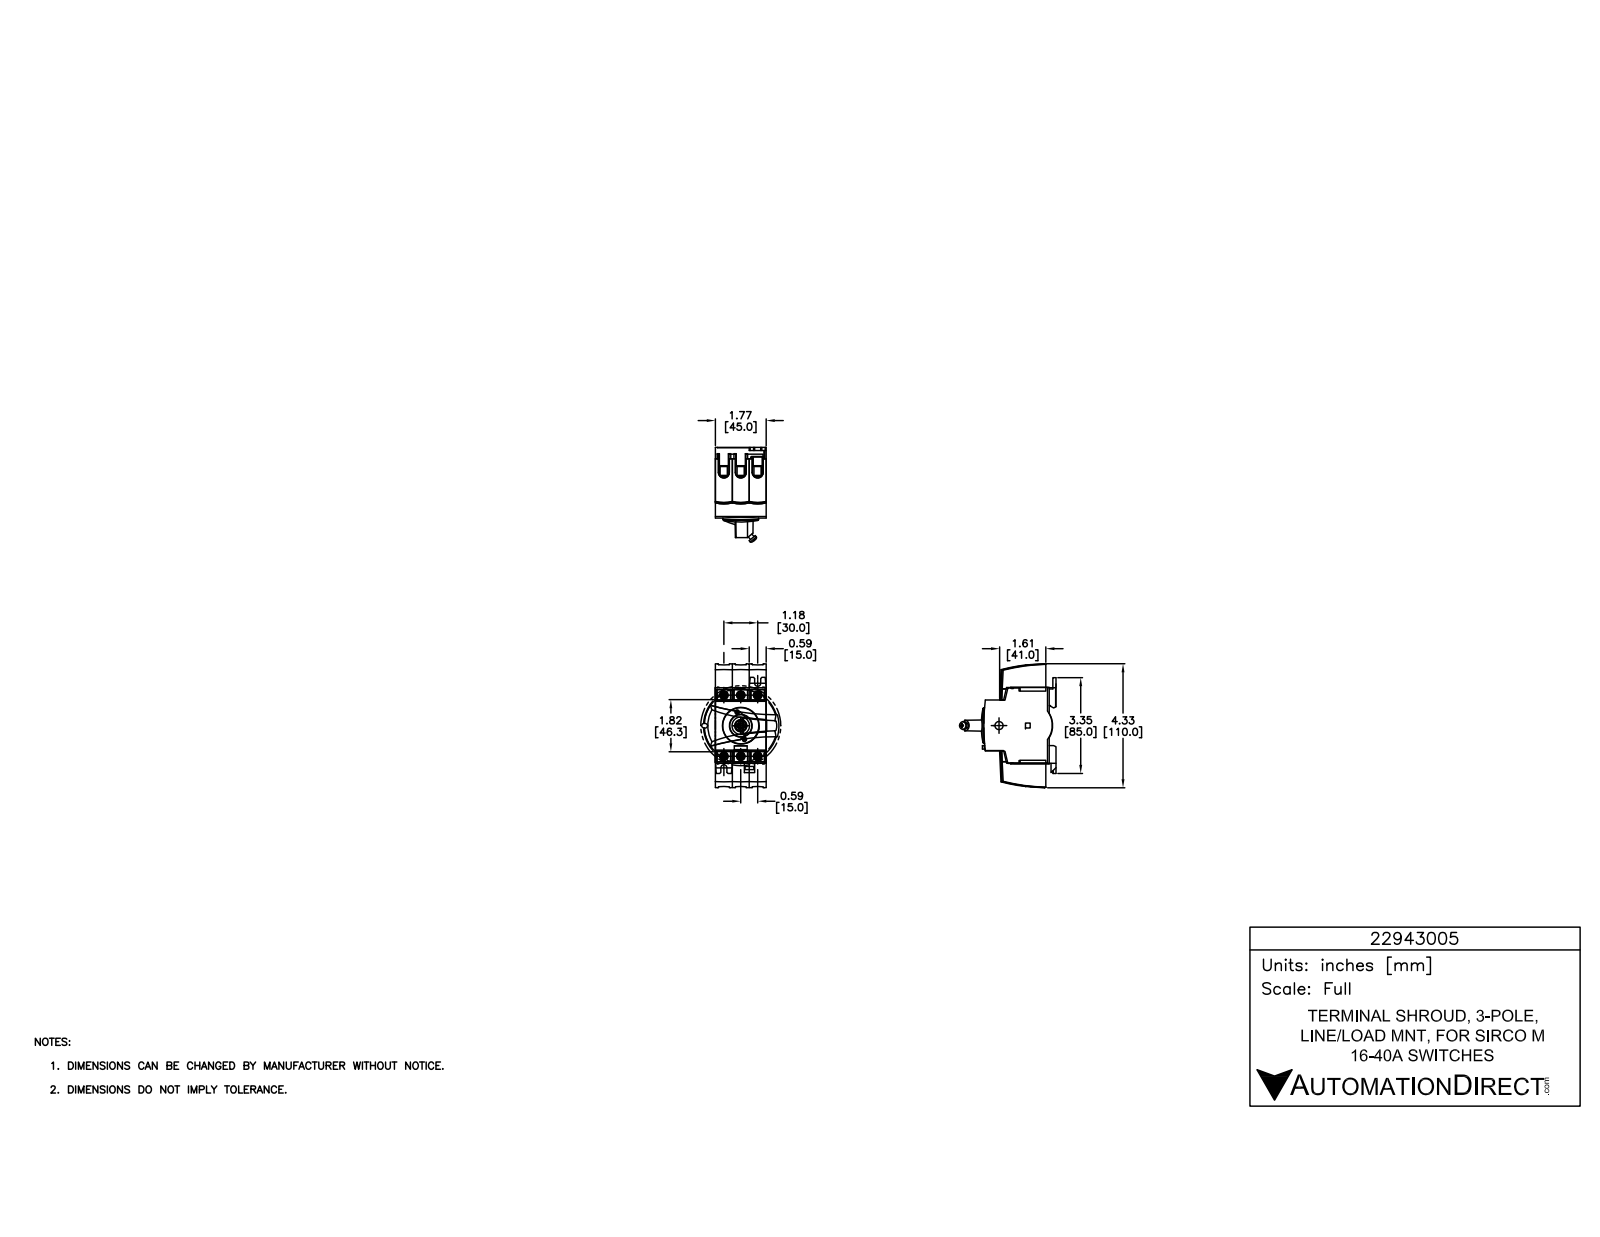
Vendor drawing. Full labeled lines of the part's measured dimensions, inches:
Part name (STEP PRODUCT): 22943005
STEP written by: SolidWorks 2015 (AUTOMOTIVE_DESIGN)
Units: inches
Bodies: 1 solid, 81 faces (45 planar, 6 cylindrical, 30 other)
Overall size (bounding box): 1.772 × 1.575 × 1.262
Volume: 0.417 in³ · Surface area: 17.97 in²
Partial cylindrical surfaces — rounded edges, fillets, slot ends (radius × count): R0.189 ×3, R0.228 ×3
Main face-to-face distances: 0.047, 0.567, 1.157, 0.591, 1.724, 0.52, 0.614, 1.11, 1.205, 1.772
